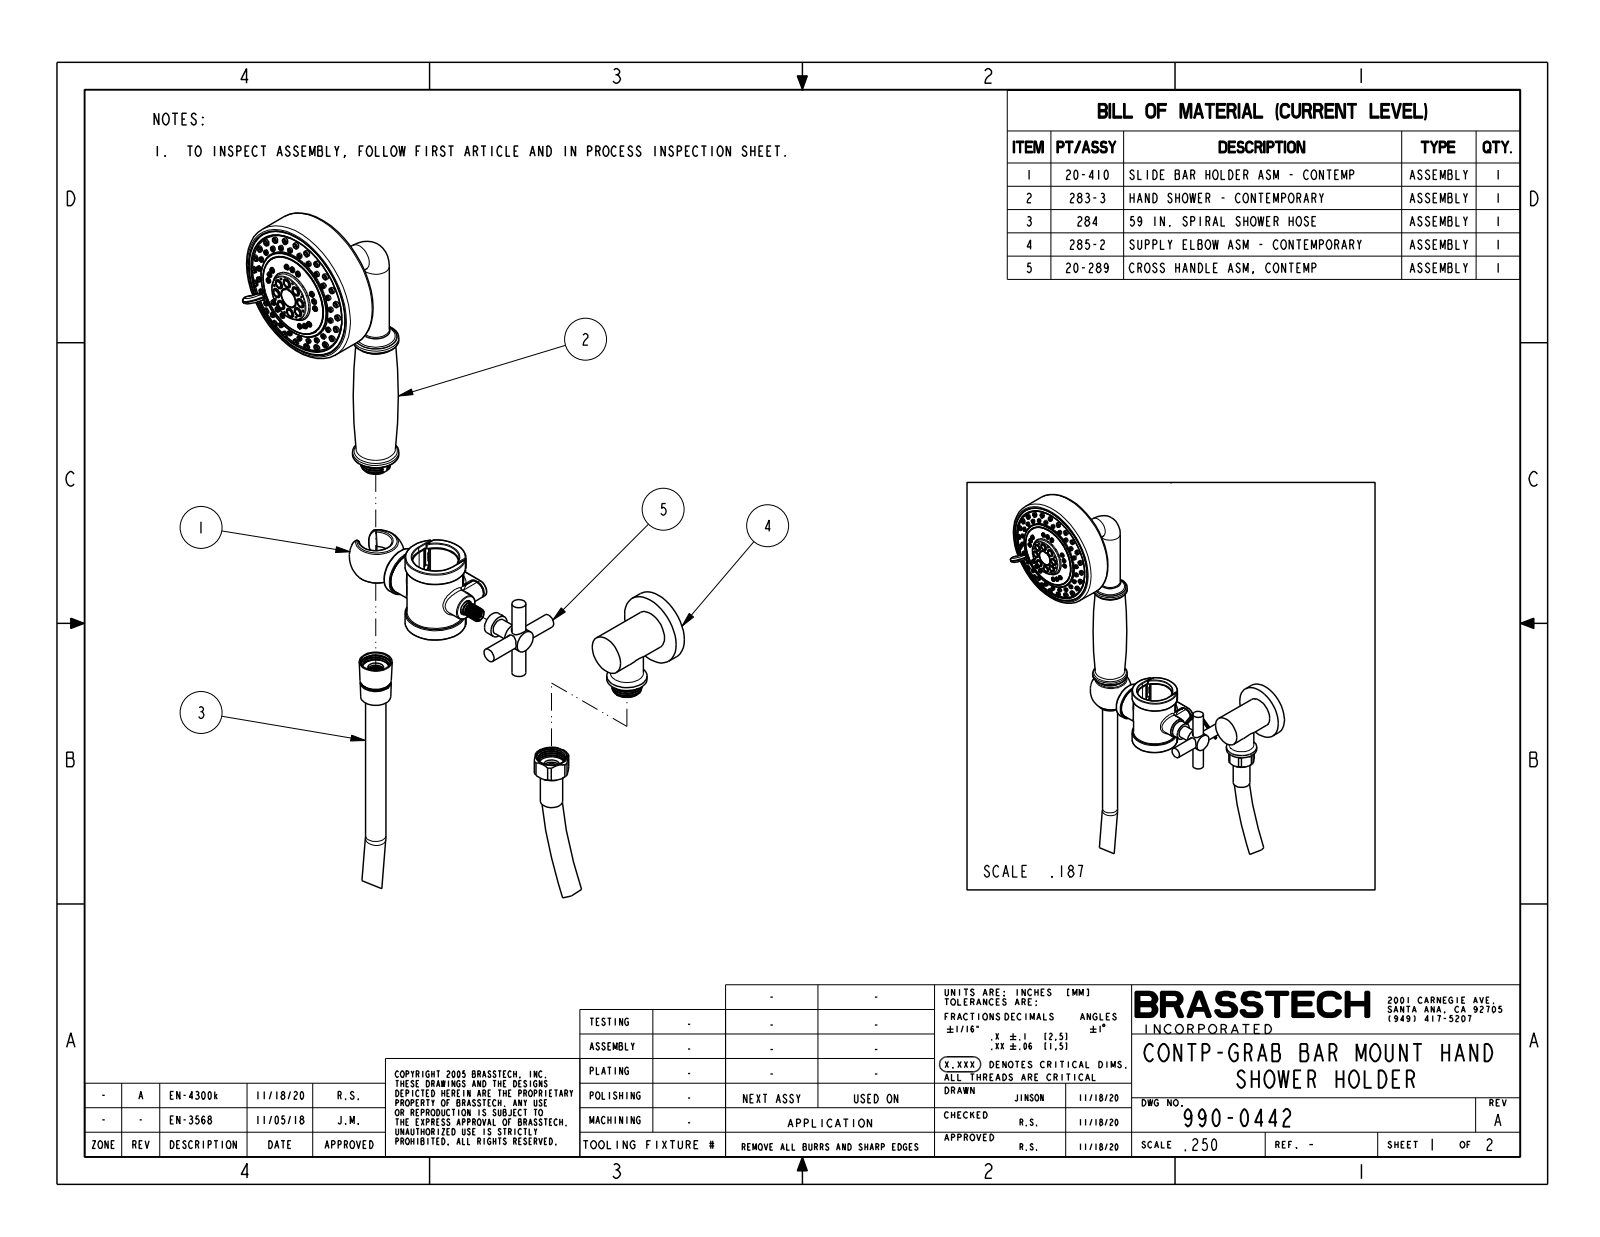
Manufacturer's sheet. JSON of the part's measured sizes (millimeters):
{"part_name": "990-0442", "step_written_by": "CREO PARAMETRIC BY PTC INC, 2018400 (CONFIG_CONTROL_DESIGN)", "units": "millimeters", "bodies": {"solids": 1, "faces": 1390, "planar": 193, "cylindrical": 329, "other": 868}, "overall_size": [752, 382.7, 142.7], "volume_mm3": 700200, "surface_area_mm2": 154200, "round_holes": [[1.5, 8], [10.3, 2], [27.4, 1], [32.1, 1], [33, 1], [35.6, 1]], "round_bosses_or_shafts": [[3.6, 39], [4.2, 23], [14.2, 3], [19.1, 2], [9.8, 2], [101.6, 1], [59, 1], [50.8, 1]], "partial_cylinders_radius": [[0.5, 44], [0.5, 4], [0.8, 4], [1.5, 4], [1.6, 4], [0.8, 2], [6.4, 2], [2, 1]], "face_to_face_distances": [98.1, 8.1, 106.2, 8.4, 106.5, 43.4, 51.8, 51.5, 54.7, 30.1], "hole_center_spacings": [11.3, 20.8, 27.2, 29.4, 11.3, 27.2, 20.8, 20.8]}
